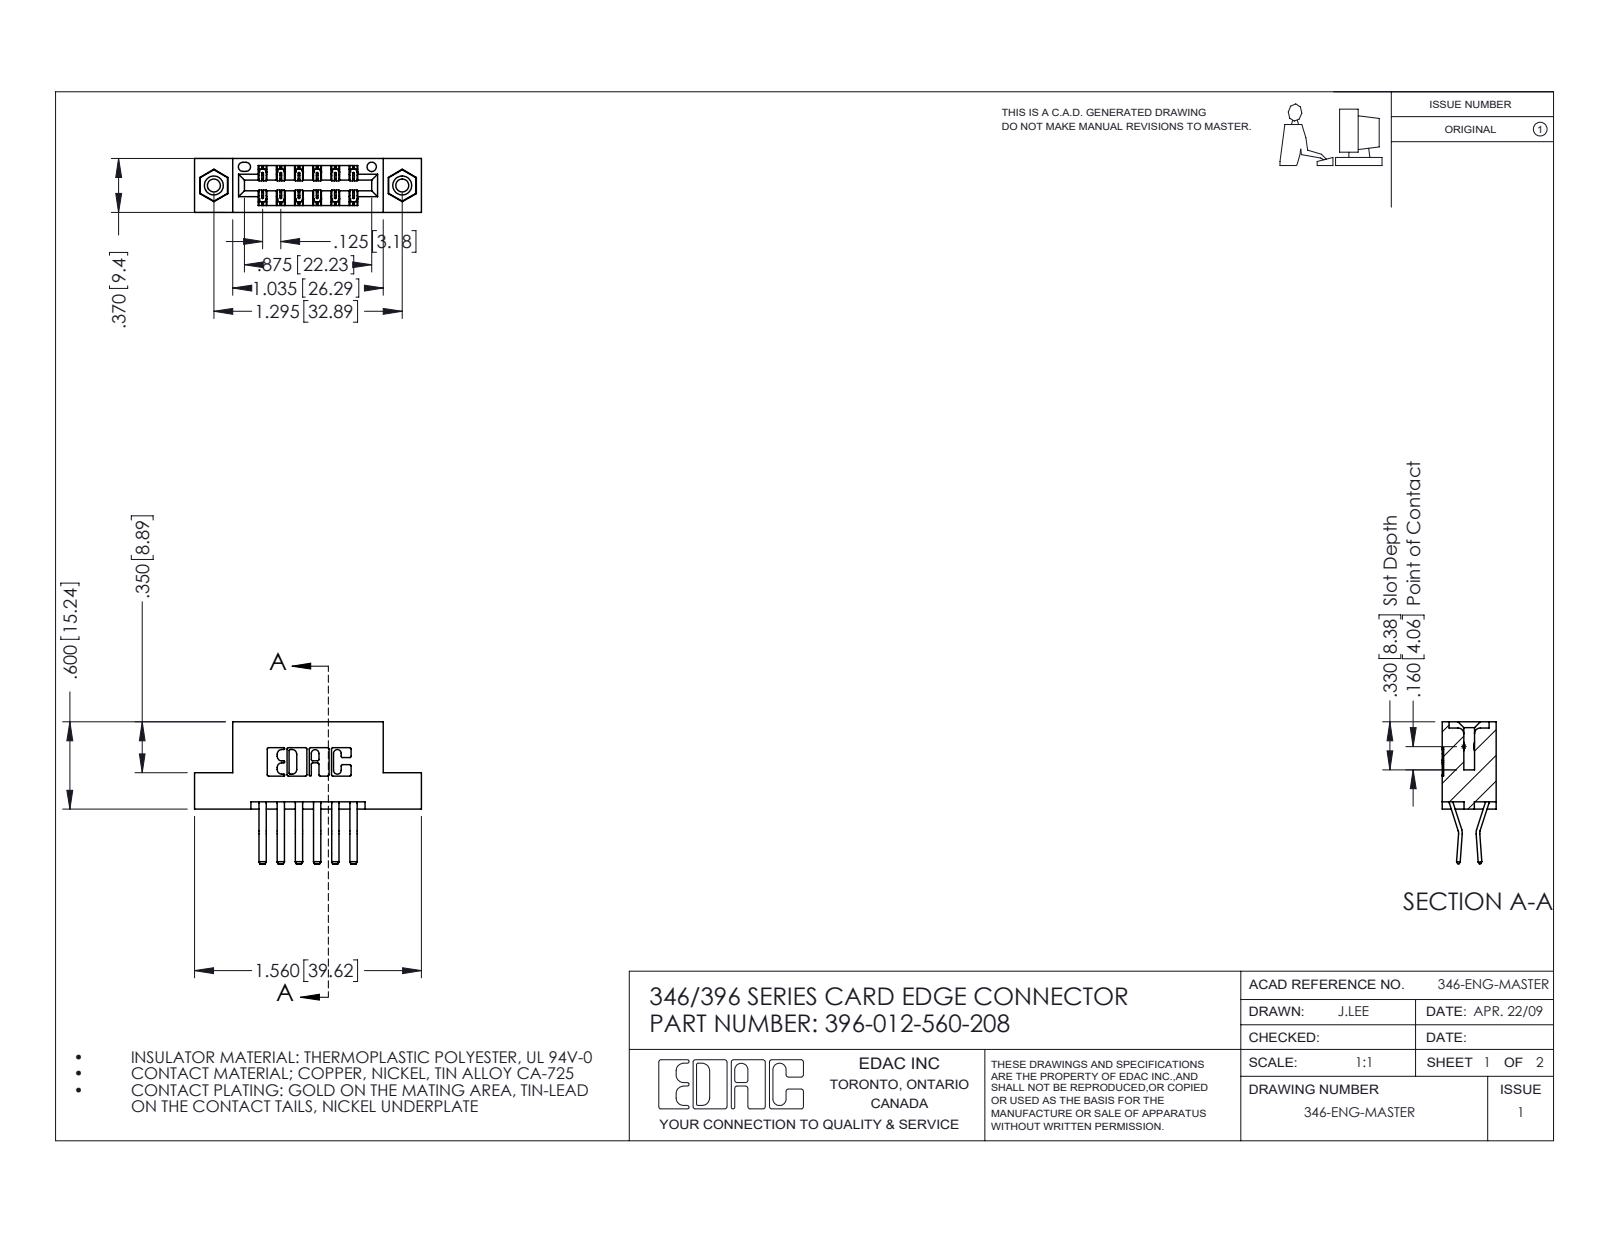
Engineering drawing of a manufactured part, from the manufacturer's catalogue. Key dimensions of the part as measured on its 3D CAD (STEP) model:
Part name (STEP PRODUCT): 345-292-001_560 Tail; 396-012-560-208; 346 Part_Flush Mounting Lugs - 0.156 Dia-TI; 345-250-001_345-250-003-102
STEP written by: SolidWorks 2016 (CONFIG_CONTROL_DESIGN)
Units: inches
Bodies: 15 solids, 830 faces (528 planar, 286 cylindrical, 16 other)
Overall size (bounding box): 1.56 × 0.975 × 0.37
Volume: 0.223 in³ · Surface area: 7.269 in²
Round holes (diameter × count): ⌀0.089 ×2, ⌀0.125 ×2, ⌀0.156 ×2, ⌀0.064 ×1
Round bosses / shafts (diameter × count): ⌀0.155 ×2
Partial cylindrical surfaces — rounded edges, fillets, slot ends (radius × count): R0.01 ×22, R0.006 ×18, R0.007 ×6, R0.031 ×6, R0.026 ×3, R0.01 ×2, R0.014 ×2, R0.022 ×2
Main face-to-face distances: 0.25, 0.37, 0.048, 0.322, 0.025, 0.125, 0.148, 0.222, 0.1, 0.174
Hole centre spacings: 0.246, 1.092, 1.295
